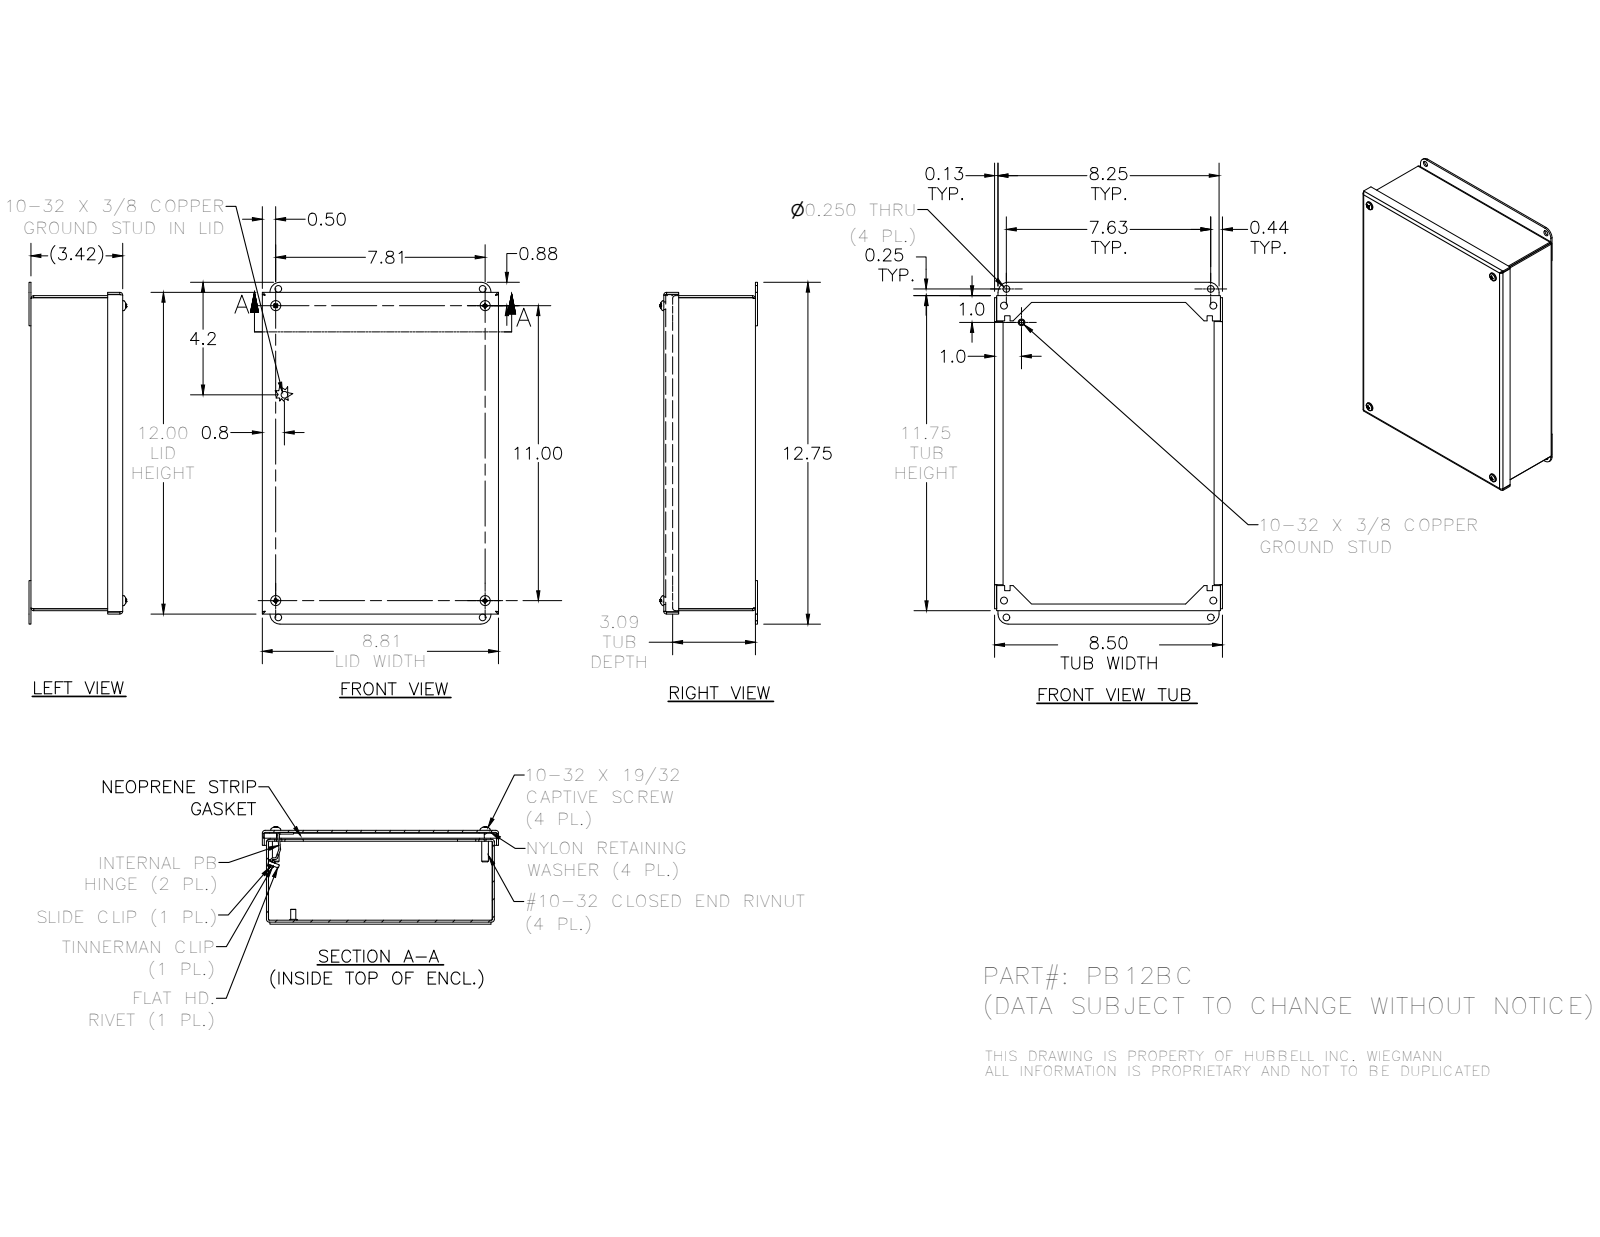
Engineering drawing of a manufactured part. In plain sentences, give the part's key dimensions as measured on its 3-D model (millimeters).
The part is named "3285; 39077; 316245; 31817 (+8 more)". Its 3-D file was written by "Autodesk Inventor 2016 (AUTOMOTIVE_DESIGN)". It is 25 solids with 609 faces: 363 planar, 132 cylindrical and 114 other. Overall it measures 323.85 by 223.84 by 92.1 millimeters. Its volume is 539 513 cubic millimeters and its surface area 549 641 square millimeters. Round holes: 4 of diameter 3.96, 4 of diameter 4.98, 4 of diameter 6.35, 4 of diameter 6.53, 4 of diameter 7.06, 4 of diameter 7.14, 4 of diameter 7.95, 2 of diameter 3.56. Round bosses or shafts: 6 of diameter 4.83, 4 of diameter 11.51, 4 of diameter 10.31, 4 of diameter 9.47, 4 of diameter 6.3, 3 of diameter 6.35, 1 of diameter 3.17. Partial cylindrical surfaces (rounded edges, fillets, slot ends): 12 of radius 0.79, 12 of radius 2.67, 6 of radius 4.78, 4 of radius 2.27, 4 of radius 2.29, 4 of radius 9.53, 3 of radius 0.8, 3 of radius 1.59. The main face-to-face distances are 1.88, 85.04, 86.92, 83.16, 214.02, 212.14, 215.9, 0.81, 3.76, 88.8. The hole center spacings are 279.4, 342.68, 16.05, 279.37, 295.28, 295.29, 354.43, 198.4.
